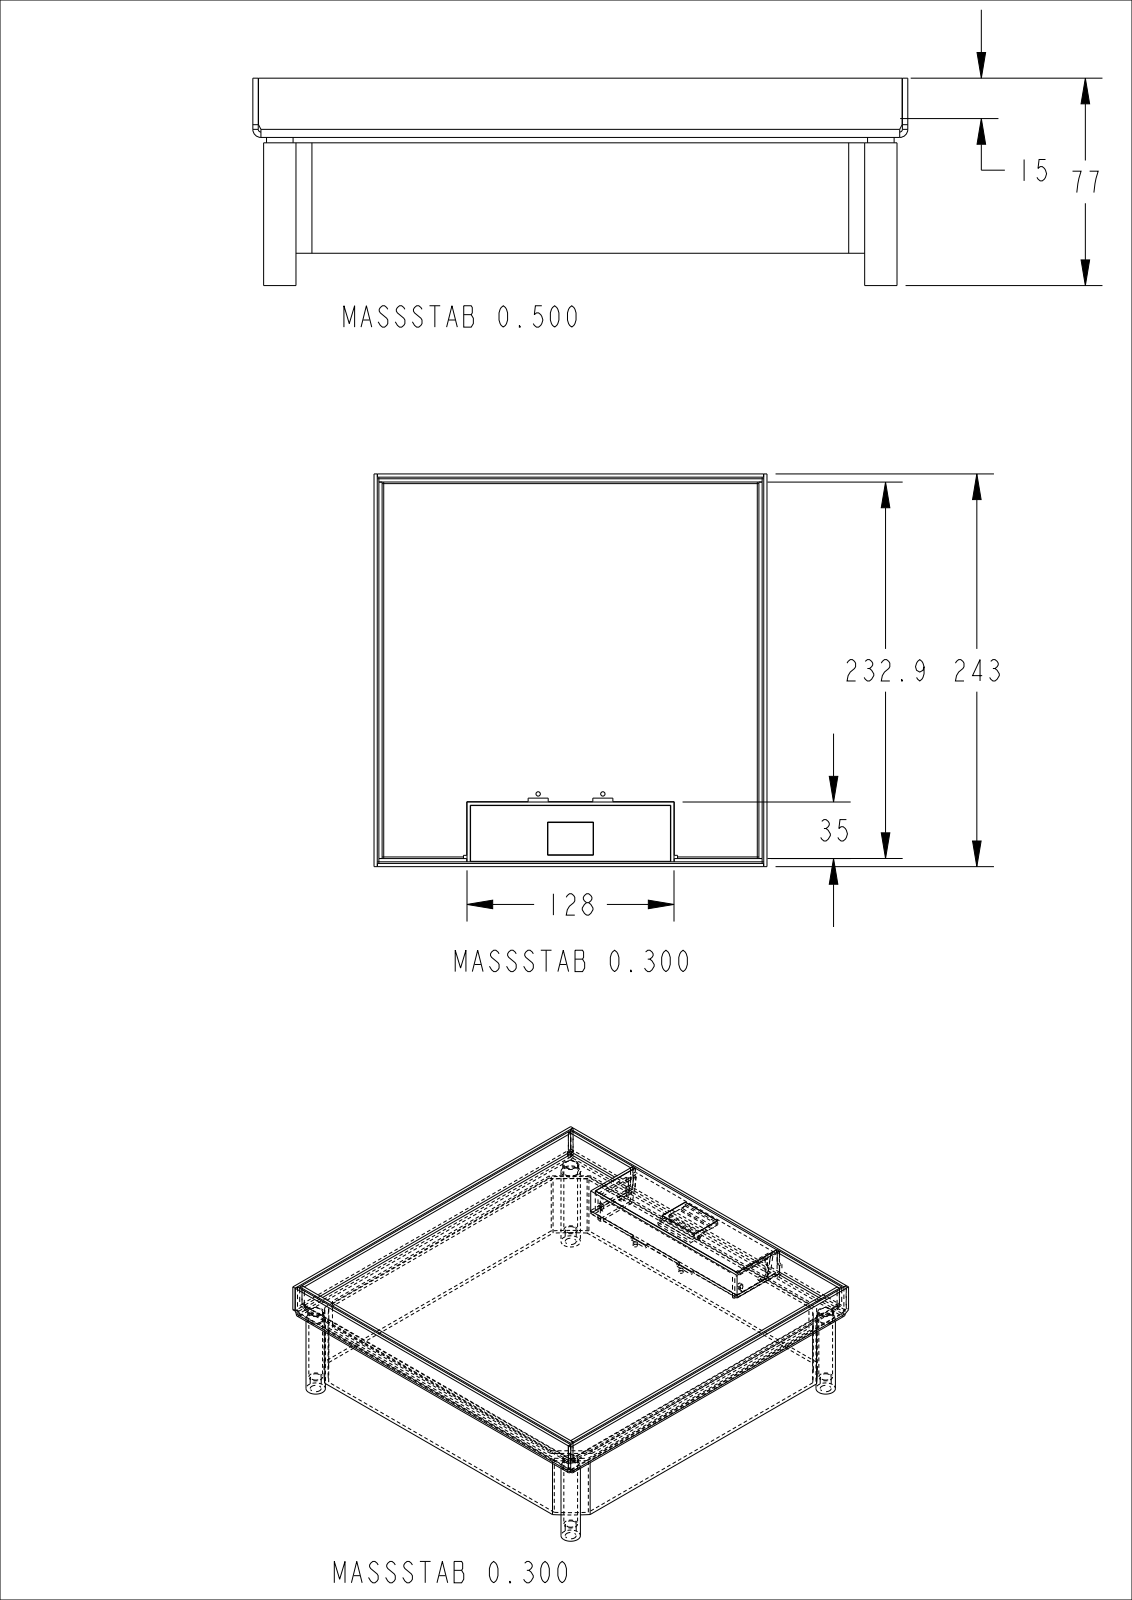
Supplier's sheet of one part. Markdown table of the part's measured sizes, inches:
| quantity | value |
| --- | --- |
| part name | T-00626_1; T-00632_1; T-00625_1; T-00823_ASM_1_ASM (+8 more) |
| STEP written by | CREO PARAMETRIC BY PTC INC, 2022281 (AUTOMOTIVE_DESIGN) |
| units | inches |
| bodies | 10 solids, 287 faces (216 planar, 63 cylindrical, 8 other) |
| overall size | 9.567 × 9.567 × 3.031 |
| volume | 18.58 in³ |
| surface area | 461.4 in² |
| round holes (diameter × count) | 0.268 × 4, 0.335 × 4, 0.106 × 2 |
| round bosses / shafts (diameter × count) | 0.472 × 4, 0.388 × 4 |
| partial cylindrical surfaces (radius × count) | 0.039 × 8, 0.118 × 8, 0.26 × 1, 5.906 × 1, 6.004 × 1 |
| main face-to-face distances | 0.079, 0.118, 0.098, 0.197, 9.252, 9.37, 9.035, 9.134, 0.236, 9.488 |
| hole center spacings | 8.78, 3.857, 5.357, 8.231, 9.033, 12.416, 1.575 |
